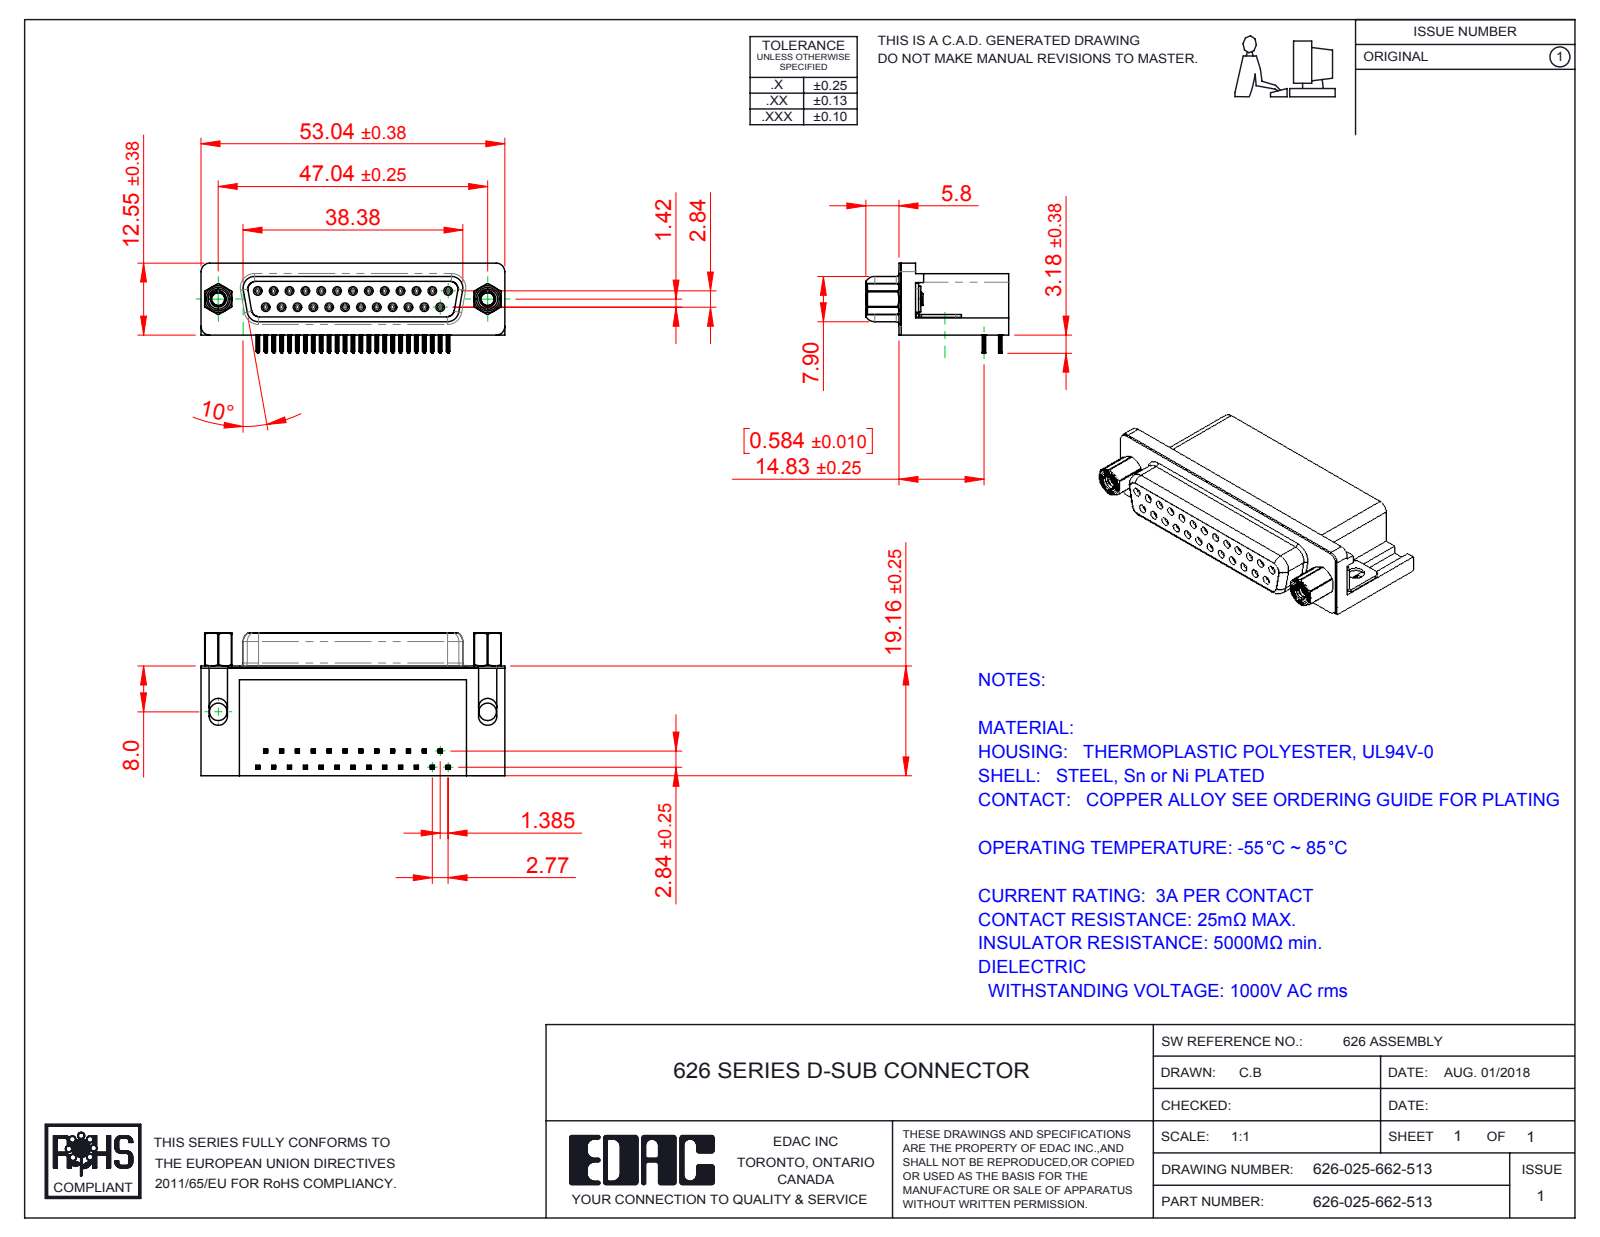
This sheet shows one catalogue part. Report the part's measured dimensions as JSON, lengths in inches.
{"part_name": "626 Shell_25 Socket; 626 Housing_25 Socket; 626 Round Threaded Standoff; 626 Contact Top (+4 more)", "step_written_by": "SolidWorks 2016 (CONFIG_CONTROL_DESIGN)", "units": "inches", "bodies": {"solids": 33, "faces": 3970, "planar": 1736, "cylindrical": 1000, "other": 1234}, "overall_size": [2.088, 0.983, 0.619], "volume_in3": 0.669, "surface_area_in2": 18.65, "round_holes": [[0.031, 25], [0.035, 25], [0.09, 2], [0.091, 2], [0.12, 2], [0.122, 2], [0.157, 2], [0.189, 2], [0.197, 2]], "round_bosses_or_shafts": [[0.047, 25], [0.193, 2], [0.185, 2], [0.177, 2], [0.152, 2], [0.11, 2]], "partial_cylinders_radius": [[0.004, 200], [0.006, 100], [0.014, 50], [0.013, 25], [0.039, 18], [0.011, 12], [0.053, 8], [0.063, 8]], "face_to_face_distances": [0.016, 0.407, 0.739, 0.107, 0.244, 0.033, 0.369, 0.125, 0.112, 0.014], "hole_center_spacings": [0.124, 0.109, 0.218, 0.327, 0.436, 0.198, 0.198, 0.294]}
